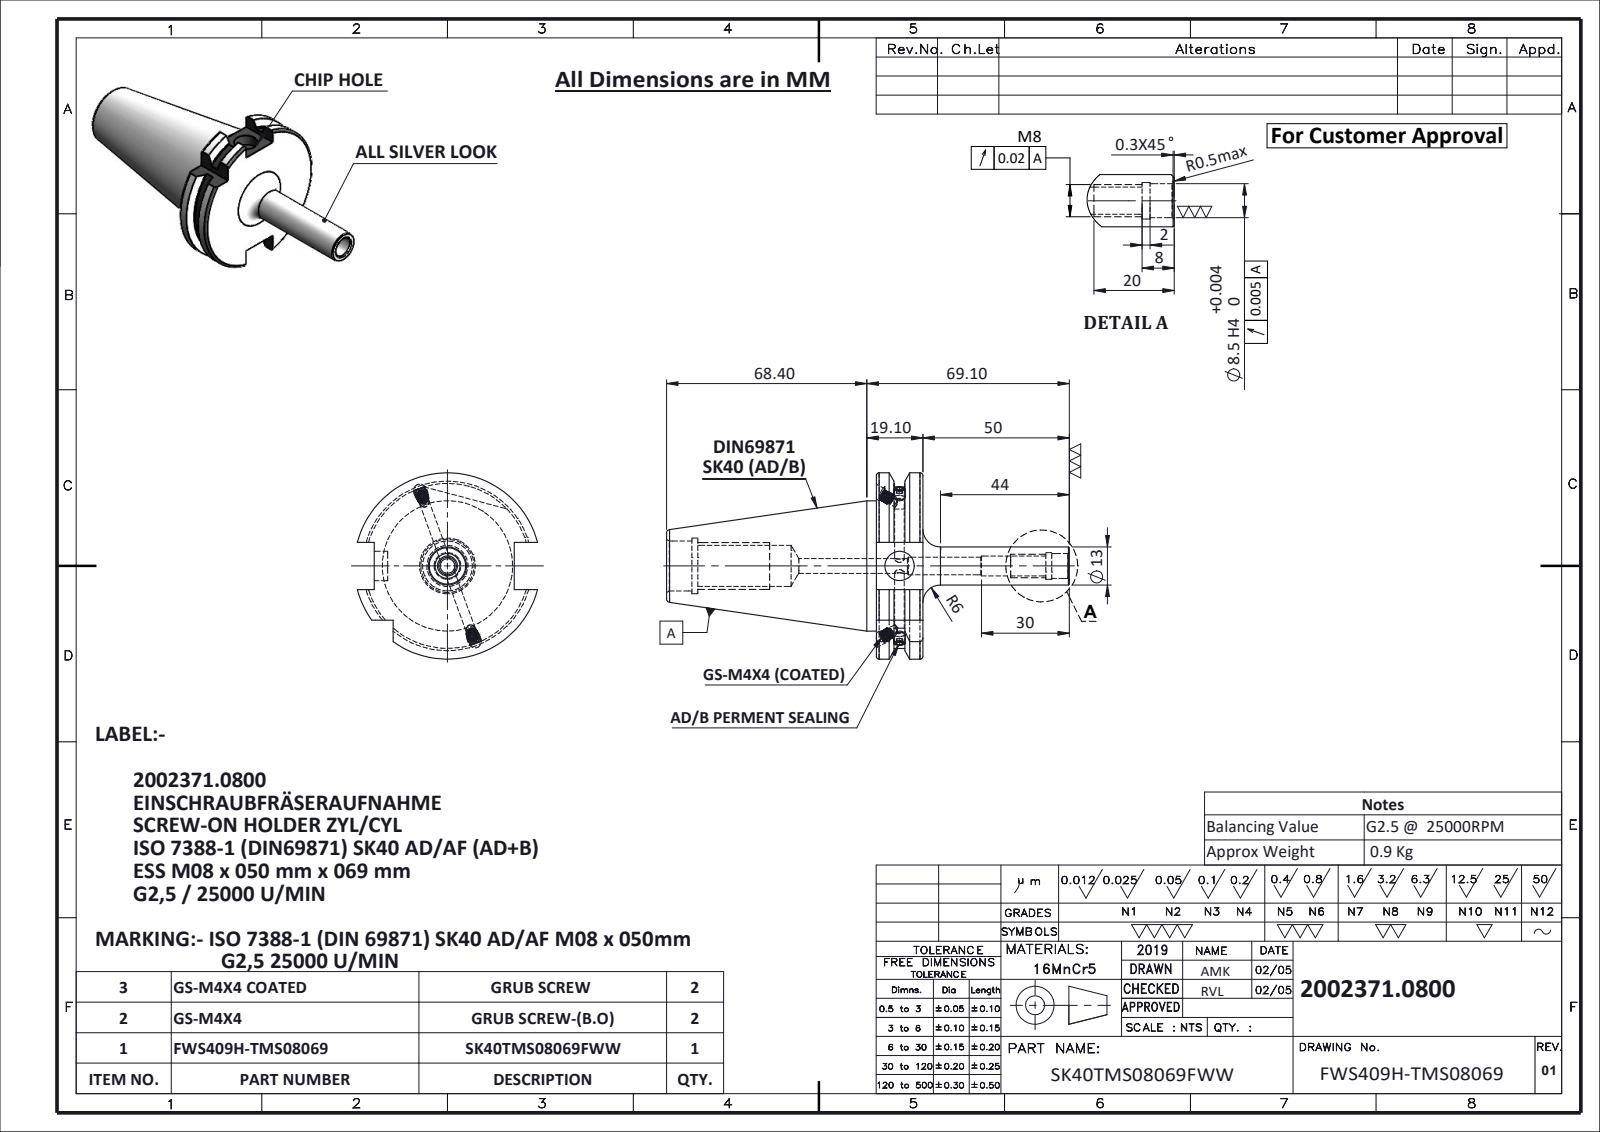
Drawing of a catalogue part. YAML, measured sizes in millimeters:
part_name: "SK40TMS08069FWW; GS-M4X4_DIN 913 - M4 x 4-N; GS-M4X4-COATING_DIN 913 - M4 x 4-N; FWS409H-TMS08069"
step_written_by: "SolidWorks 2024 (AUTOMOTIVE_DESIGN)"
units: millimeters
bodies: {solids: 5, faces: 246, planar: 64, cylindrical: 74, other: 108}
overall_size: [137.5, 63.55, 61.48]
volume: 109399
surface_area: 23702
round_holes:
  - {diameter: 3.3, count: 3}
  - {diameter: 4.5, count: 2}
  - {diameter: 5, count: 1}
  - {diameter: 6, count: 1}
  - {diameter: 6.8, count: 1}
  - {diameter: 8.5, count: 1}
  - {diameter: 9.1, count: 1}
  - {diameter: 10, count: 1}
  - {diameter: 14, count: 1}
  - {diameter: 17, count: 1}
  - {diameter: 19, count: 1}
round_bosses_or_shafts:
  - {diameter: 4, count: 4}
  - {diameter: 2.9, count: 2}
  - {diameter: 44.45, count: 1}
  - {diameter: 13, count: 1}
partial_cylinders:
  - {radius: 28.12, count: 1}
  - {radius: 31.77, count: 1}
face_to_face_distances: [15.9, 16.1, 47.8, 71.6, 87.5, 10.7, 60.9, 76.8, 77.63, 66.93]
